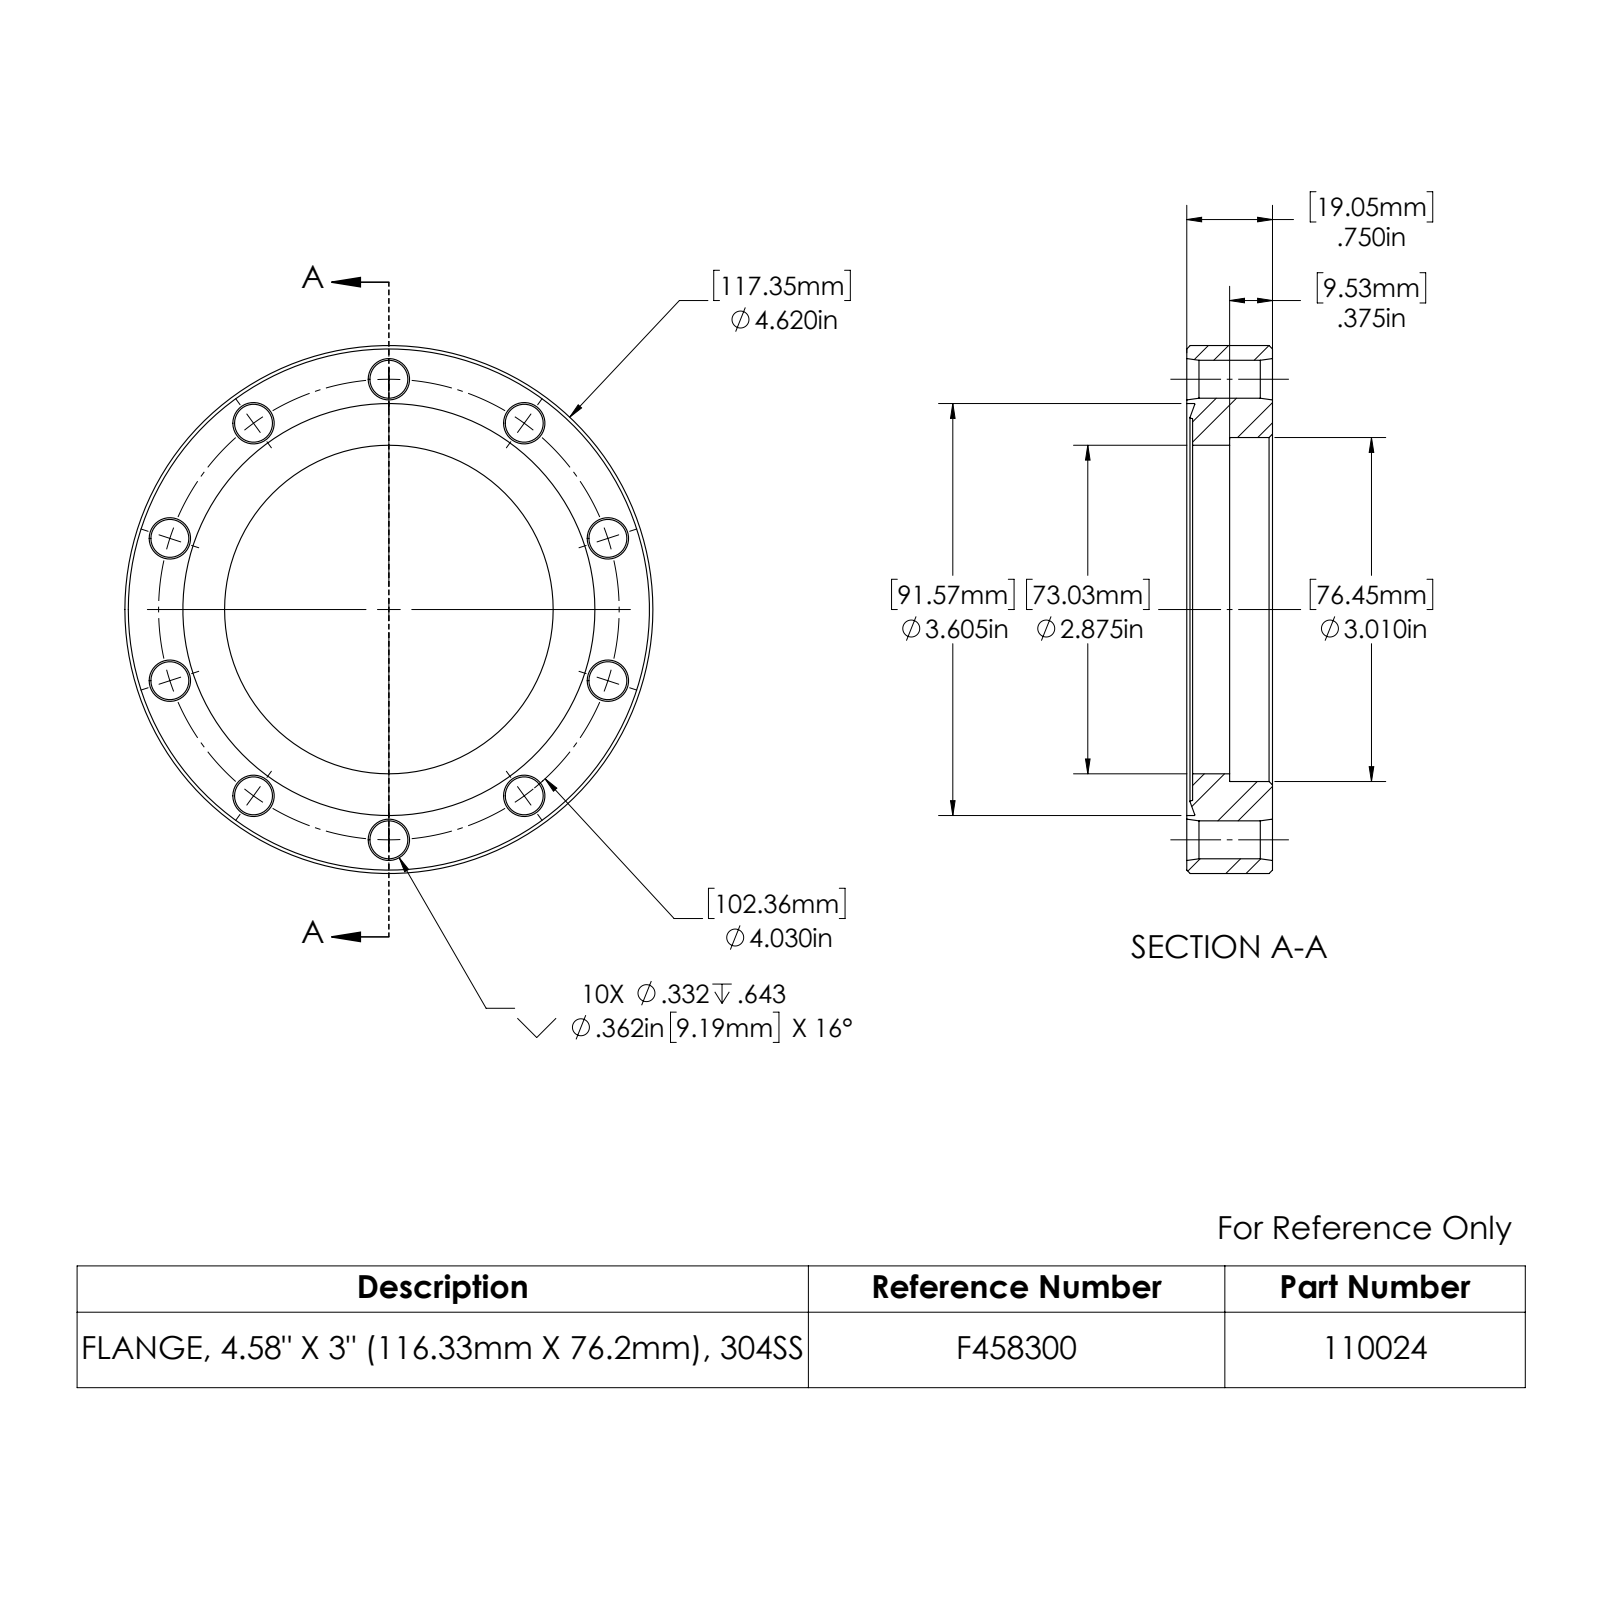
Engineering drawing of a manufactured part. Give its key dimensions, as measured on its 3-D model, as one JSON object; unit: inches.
{"part_name": "110024", "step_written_by": "SolidWorks 2022 (AUTOMOTIVE_DESIGN)", "units": "inches", "bodies": {"solids": 1, "faces": 90, "planar": 4, "cylindrical": 28, "other": 58}, "overall_size": [4.62, 4.62, 0.75], "volume_in3": 6.6, "surface_area_in2": 44.12, "round_holes": [[0.332, 10], [2.875, 1], [3.01, 1], [3.605, 1]], "round_bosses_or_shafts": [[4.62, 1]], "face_to_face_distances": [0.75, 0.051, 0.699, 0.375, 0.324, 0.375], "hole_center_spacings": [1.246, 2.015, 3.261, 3.833, 1.245, 2.015, 2.369, 2.369]}
